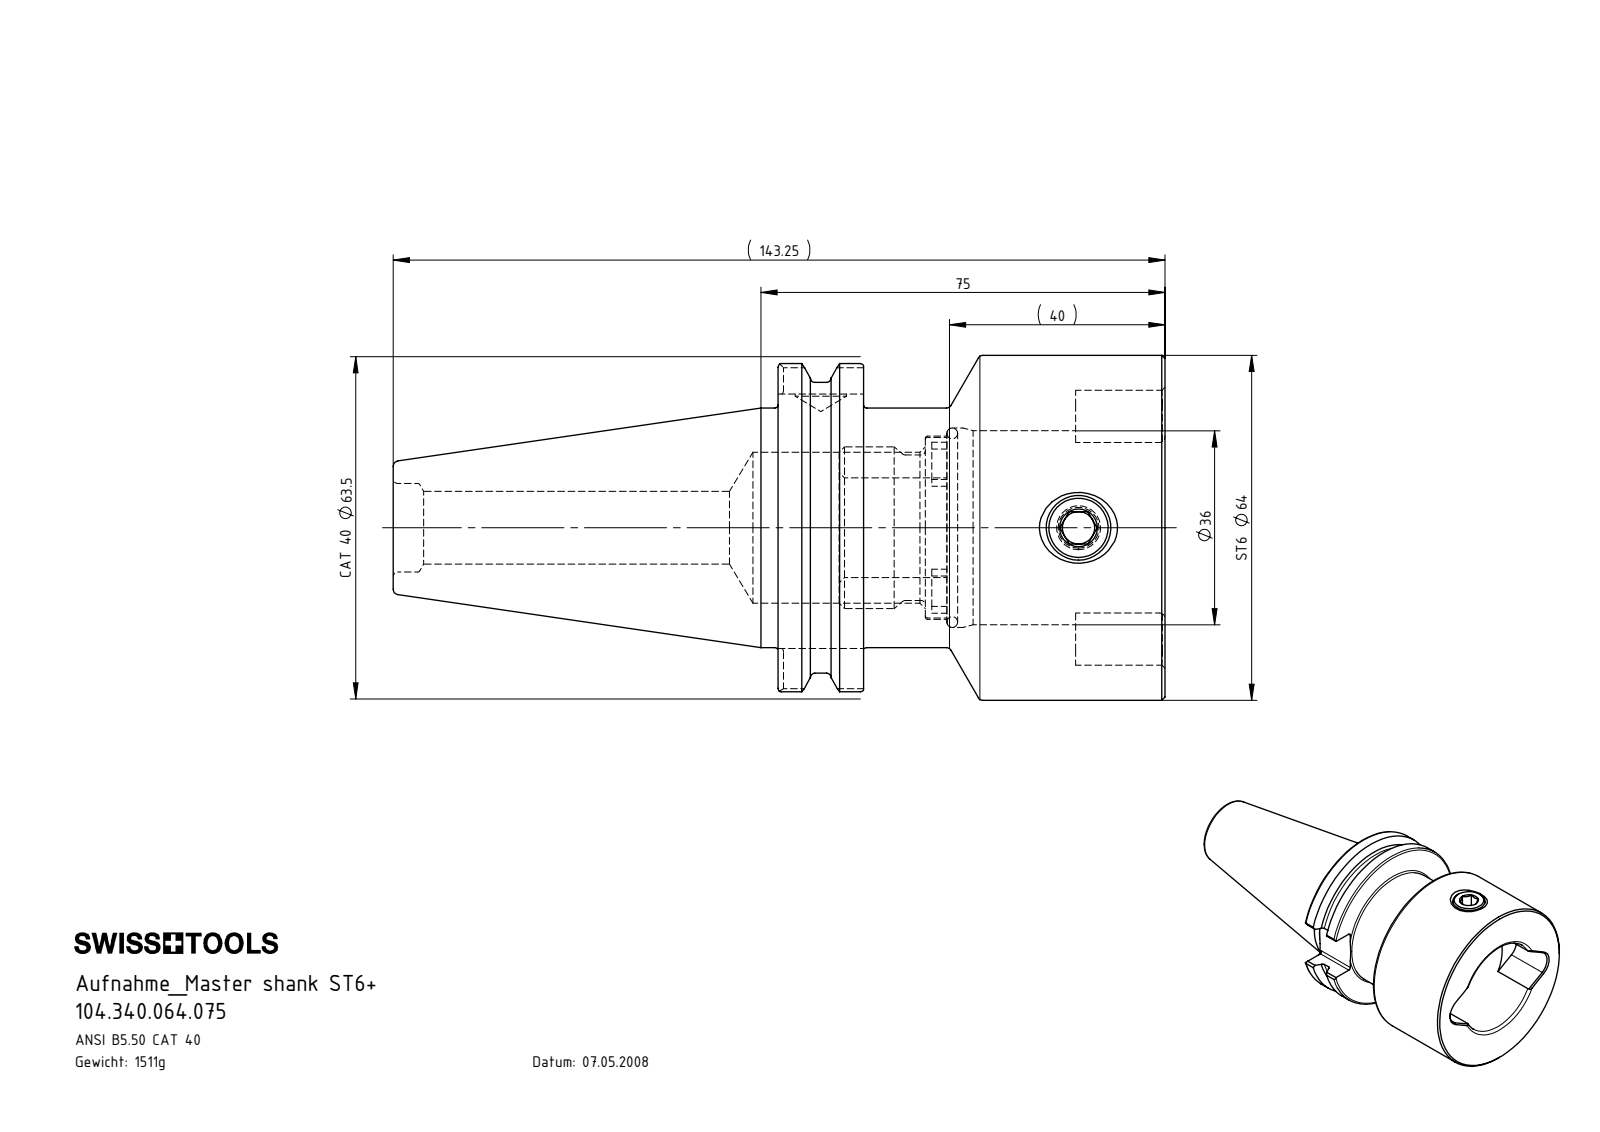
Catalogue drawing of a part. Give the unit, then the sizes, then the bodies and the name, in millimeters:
Units: millimetres
Overall size (bounding box): 143.25 × 64 × 64
Round holes (diameter × count): ⌀9.5 ×1, ⌀11 ×1, ⌀13.5 ×1, ⌀16.43 ×1, ⌀18.5 ×1, ⌀28 ×1, ⌀34 ×1, ⌀36 ×1, ⌀37 ×1
Round bosses / shafts (diameter × count): ⌀64 ×1, ⌀63.5 ×1, ⌀56.36 ×1, ⌀44.45 ×1, ⌀33.5 ×1, ⌀30 ×1, ⌀27 ×1, ⌀12 ×1
Partial cylindrical surfaces — rounded edges, fillets, slot ends (radius × count): R0.8 ×8, R5.2 ×2
Main face-to-face distances: 55.95, 15.87, 71.82, 31.32, 15.45, 40.5, 27.32, 11.45, 4, 44.5
Volume: 192 918 mm³ · Surface area: 45 888 mm²
Bodies: 4 solids, 182 faces (54 planar, 49 cylindrical, 79 other)
Part name (STEP PRODUCT): CT4-ST6.K01.075; DIN 3771 - 33x2; CT4-ST6.K01.075_A; ST6-ER4.001.020_A (+1 more)
STEP written by: SolidWorks 2015 (CONFIG_CONTROL_DESIGN)
